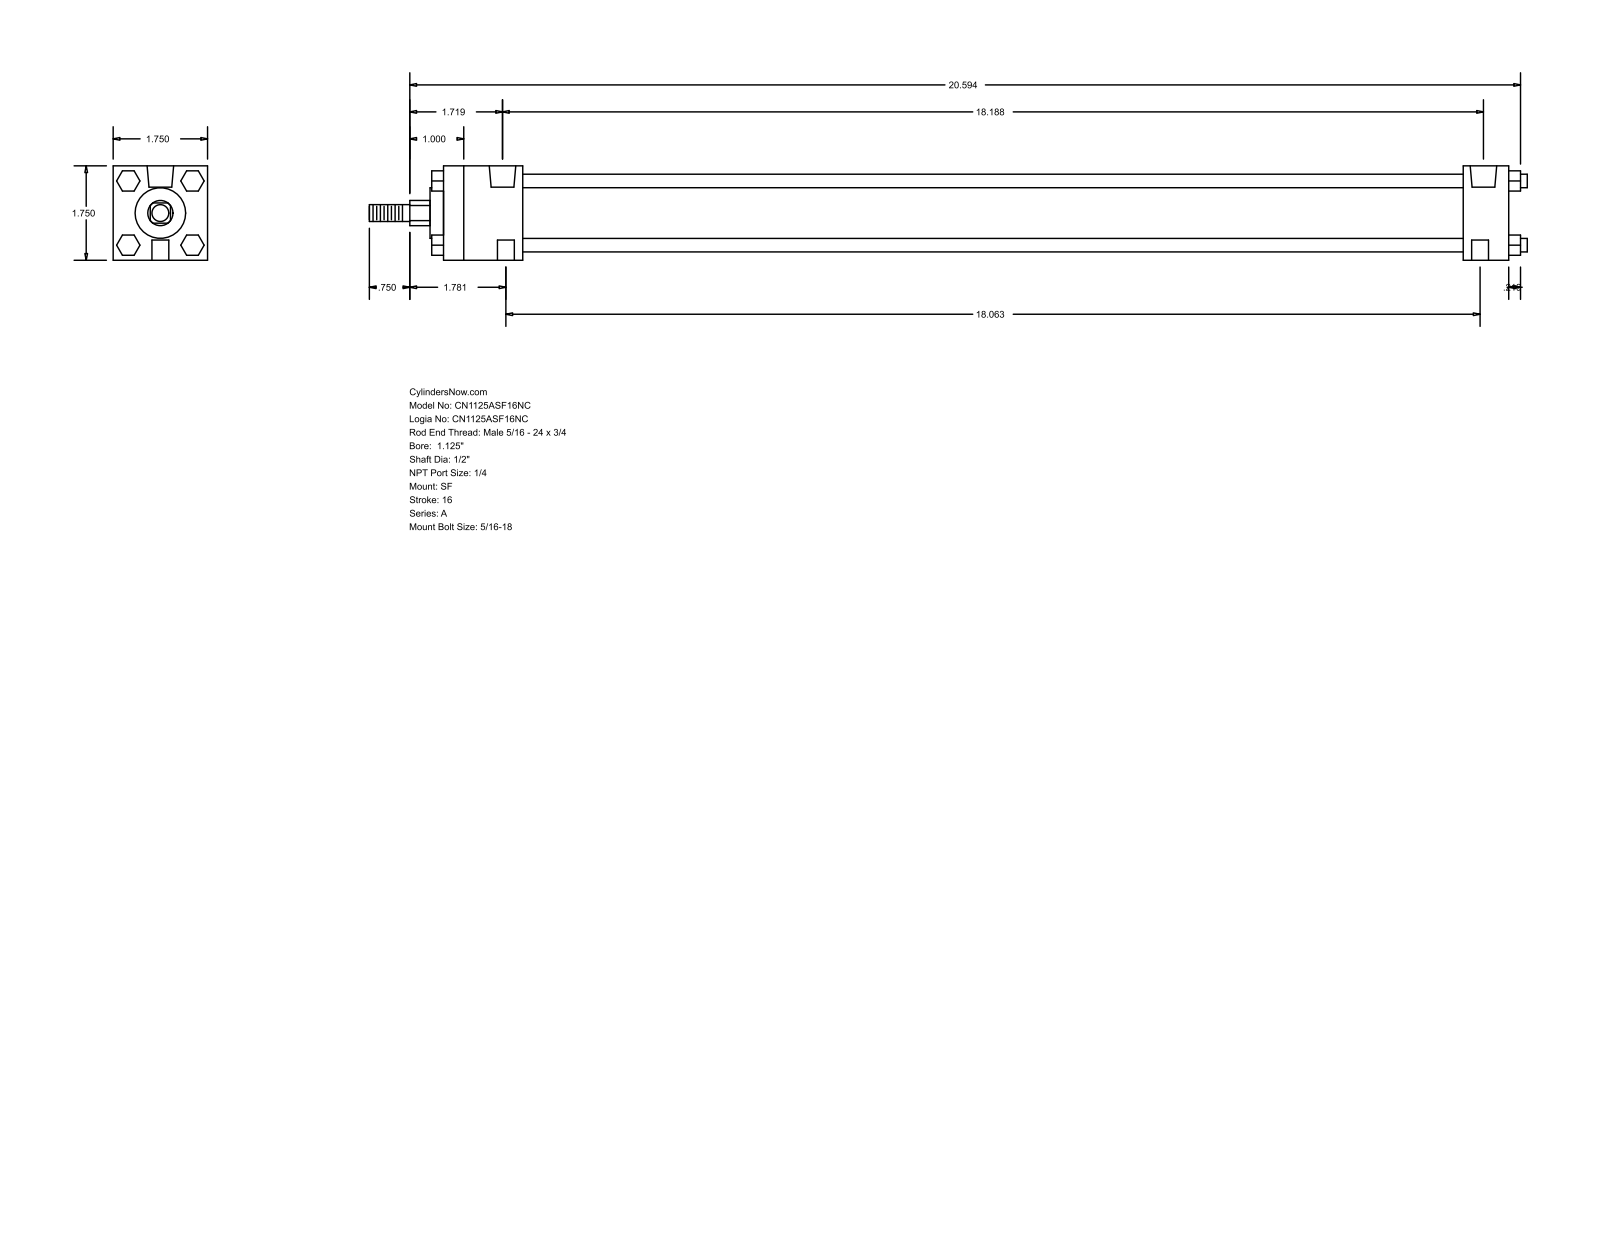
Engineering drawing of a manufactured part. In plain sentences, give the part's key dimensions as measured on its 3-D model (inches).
The part is named "A_SF__0112_0.5". Its 3-D file was written by "GSSL Pune (CONFIG_CONTROL_DESIGN)". It is 0 solids with 120 faces: 92 planar, 28 cylindrical and 0 other. Overall it measures 21.469 by 1.75 by 1.75 inches. Round holes: 2 of diameter 0.219, 2 of diameter 0.313, 2 of diameter 0.492. Round bosses or shafts: 4 of diameter 0.25, 1 of diameter 1.255, 1 of diameter 0.937, 1 of diameter 0.5, 1 of diameter 0.313. Partial cylindrical surfaces (rounded edges, fillets, slot ends): 1 of radius 0.234. The main face-to-face distances are 1.75, 19.75, 18.906, 0.844, 1.469, 17.437, 18.281, 0.375, 0.22, 0.219. The hole center spacings are 18.063, 0.062, 0.063, 18.125, 18.125, 18.187.
